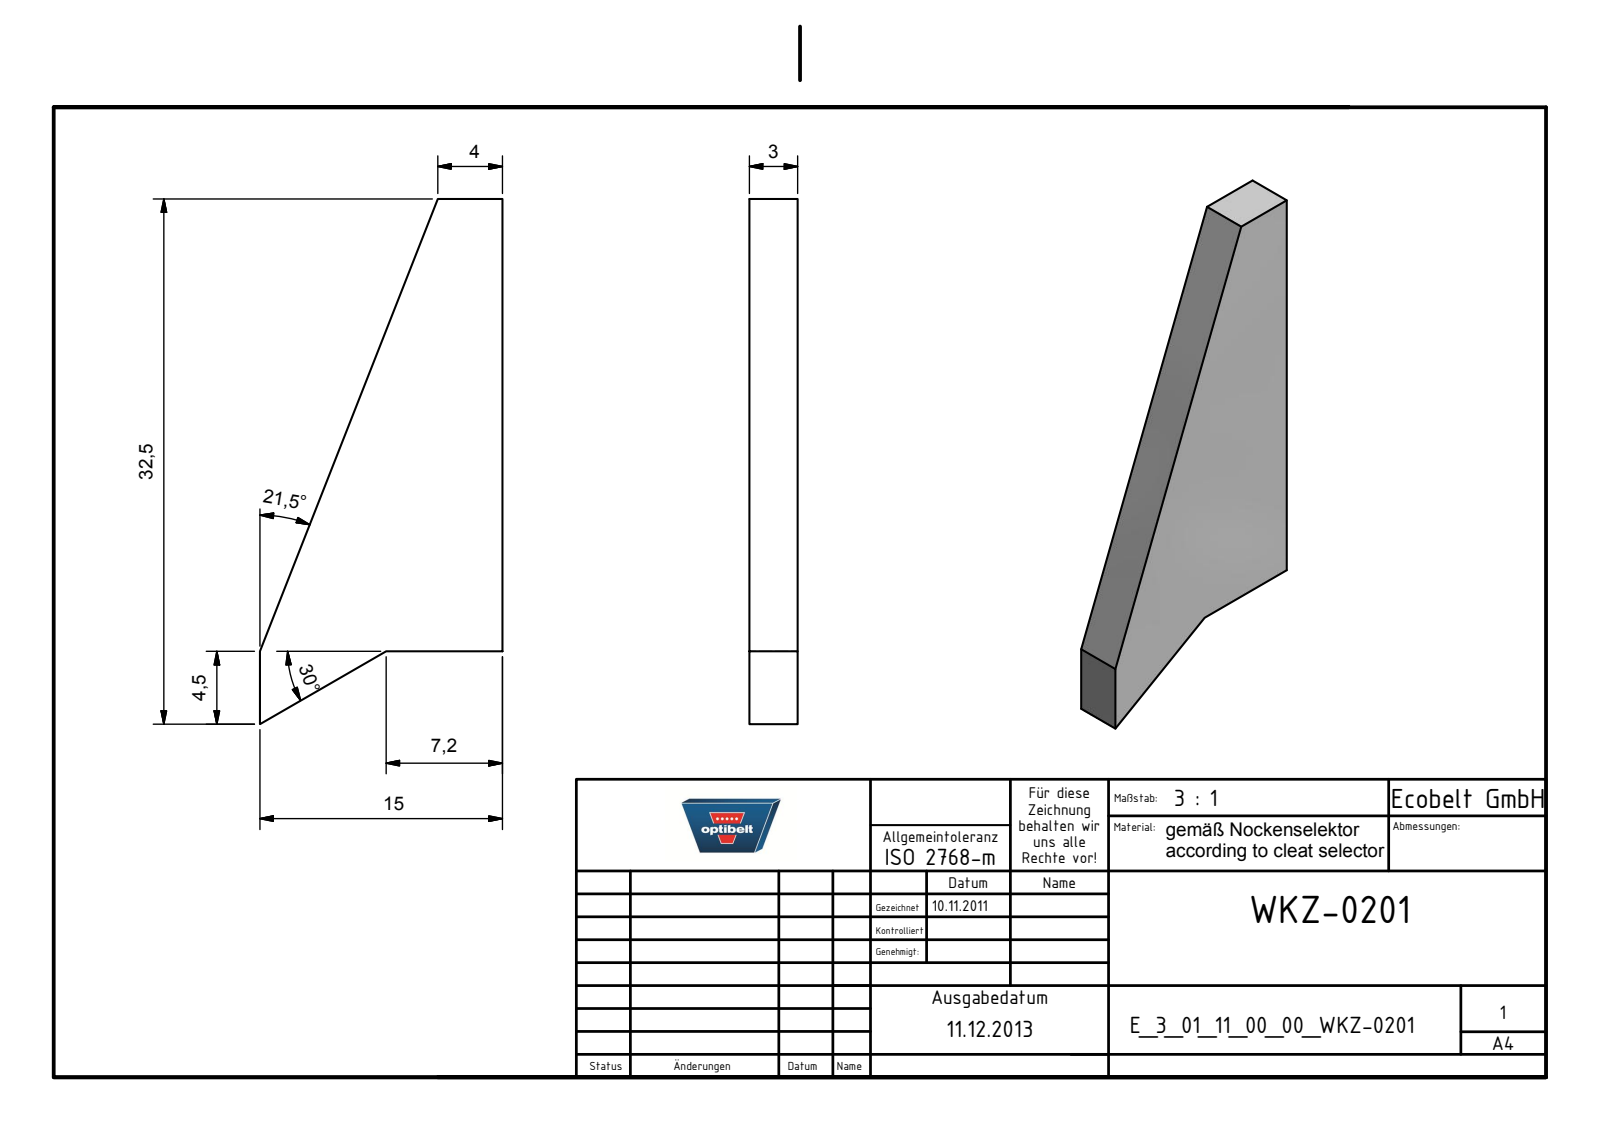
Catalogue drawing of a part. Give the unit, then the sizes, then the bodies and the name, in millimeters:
Units: millimetres
Overall size (bounding box): 32.5 × 15 × 3
Main face-to-face distances: 3, 15, 28
Volume: 850 mm³ · Surface area: 815 mm²
Bodies: 1 solid, 8 faces (8 planar, 0 cylindrical, 0 other)
Part name (STEP PRODUCT): E_3_01_11_00_00_WKZ-0201
STEP written by: Autodesk Inventor 2025 (AUTOMOTIVE_DESIGN)
